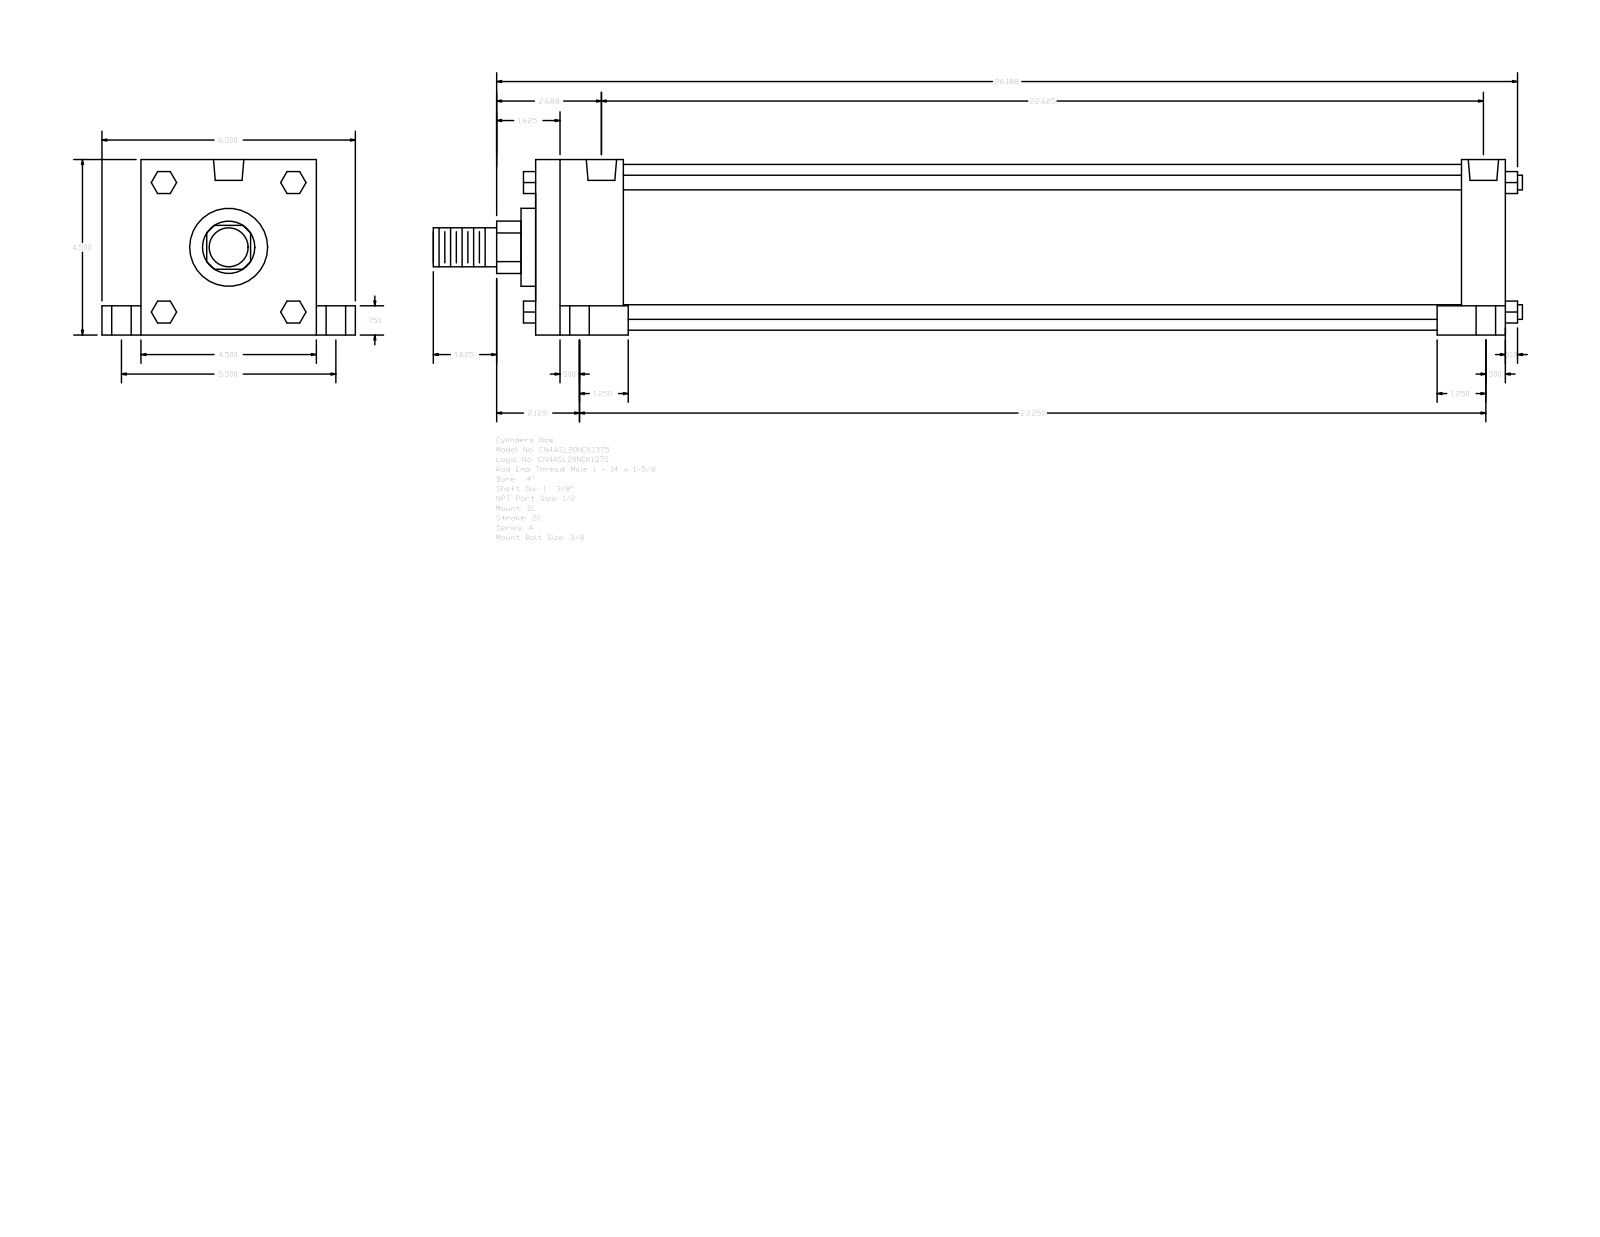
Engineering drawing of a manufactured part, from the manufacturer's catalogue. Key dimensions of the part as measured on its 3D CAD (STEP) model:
Part name (STEP PRODUCT): A_SL__0400_1.375
STEP written by: GSSL Pune (CONFIG_CONTROL_DESIGN)
Units: millimetres
Bodies: 0 solids, 150 faces (114 planar, 36 cylindrical, 0 other)
Overall size (bounding box): 709.61 × 165.1 × 114.3
Round holes (diameter × count): ⌀8.73 ×4, ⌀12.7 ×4, ⌀19.05 ×4, ⌀19.77 ×2
Round bosses / shafts (diameter × count): ⌀9.53 ×4, ⌀107.95 ×1, ⌀50.8 ×1, ⌀34.92 ×1, ⌀25.4 ×1
Partial cylindrical surfaces — rounded edges, fillets, slot ends (radius × count): R17.06 ×1
Main face-to-face distances: 114.3, 631.83, 57.15, 28.58, 25.4, 574.68, 603.25, 546.1, 139.7, 19.05
Hole centre spacings: 3.18, 69.87, 70.01, 71.29, 72, 139.7, 568.32, 571.5
